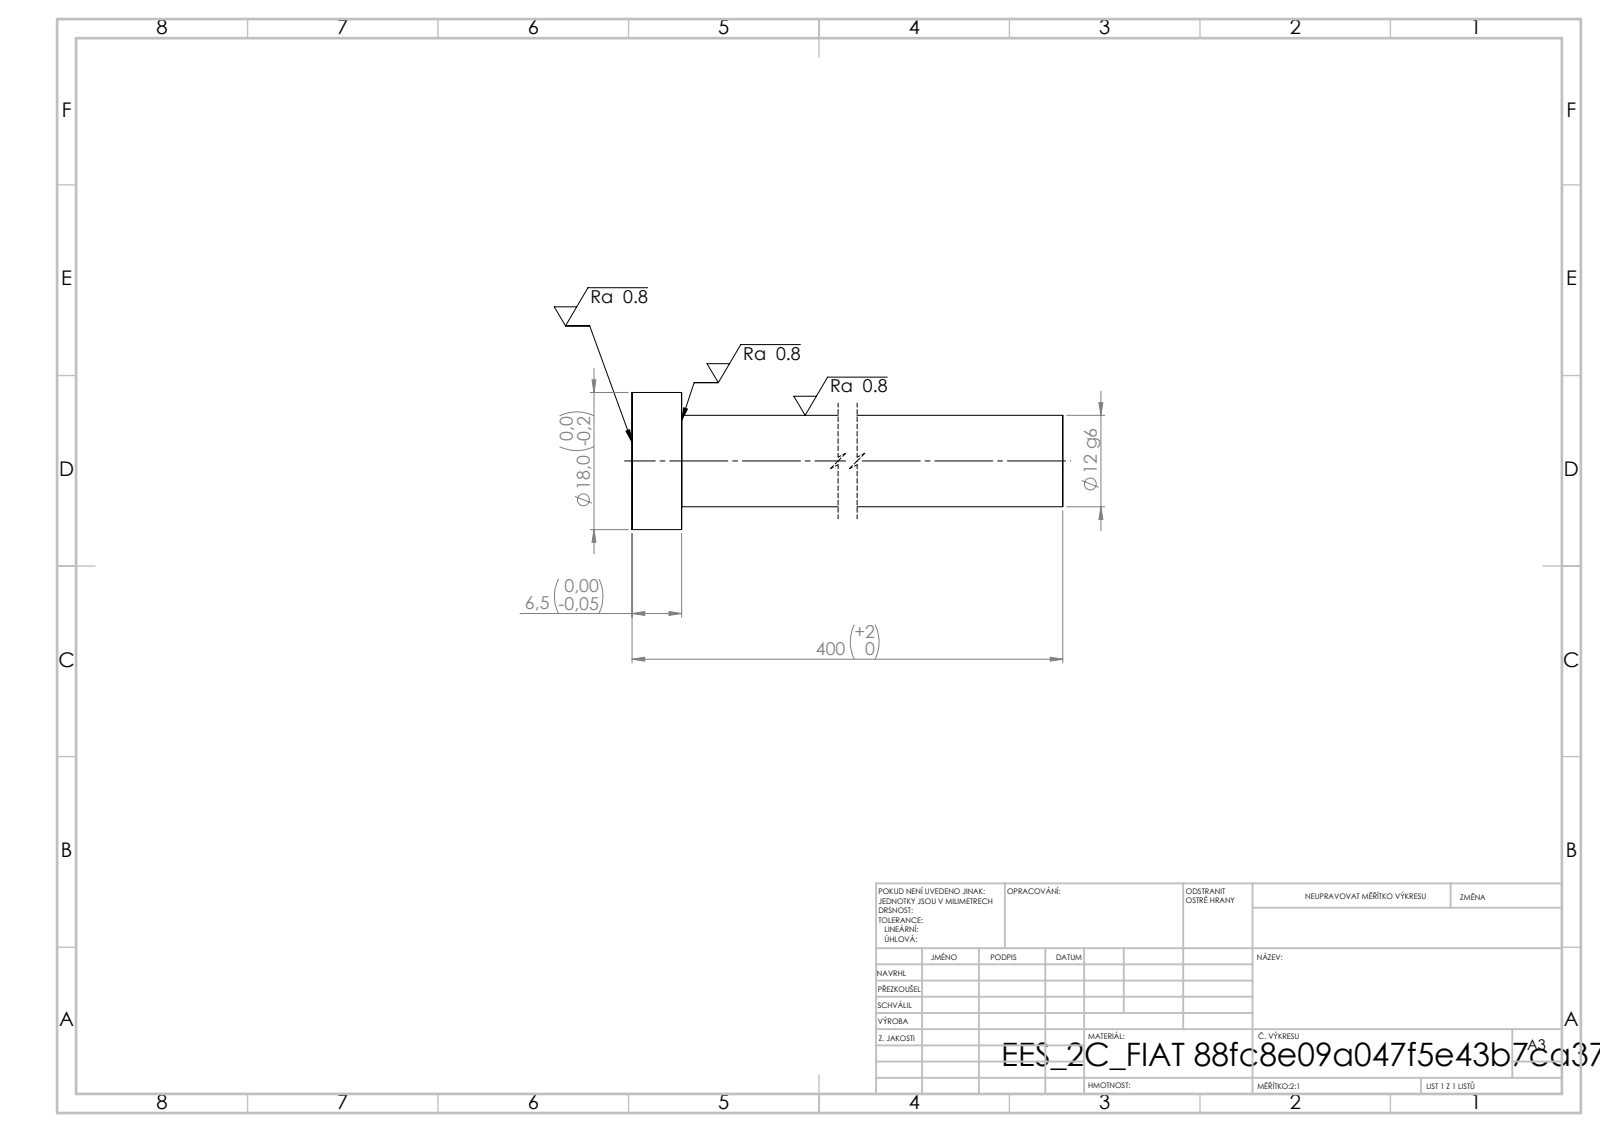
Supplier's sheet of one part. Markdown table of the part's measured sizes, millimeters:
| quantity | value |
| --- | --- |
| STEP written by | SolidWorks 2019 (CONFIG_CONTROL_DESIGN) |
| units | millimeters |
| bodies | 1 solid, 7 faces (3 planar, 4 cylindrical, 0 other) |
| overall size | 400 × 18 × 18 |
| volume | 46 158 mm³ |
| surface area | 15 711 mm² |
| round bosses / shafts (diameter × count) | 18 × 1, 12 × 1 |
| main face-to-face distances | 6.5, 400, 393.5 |
